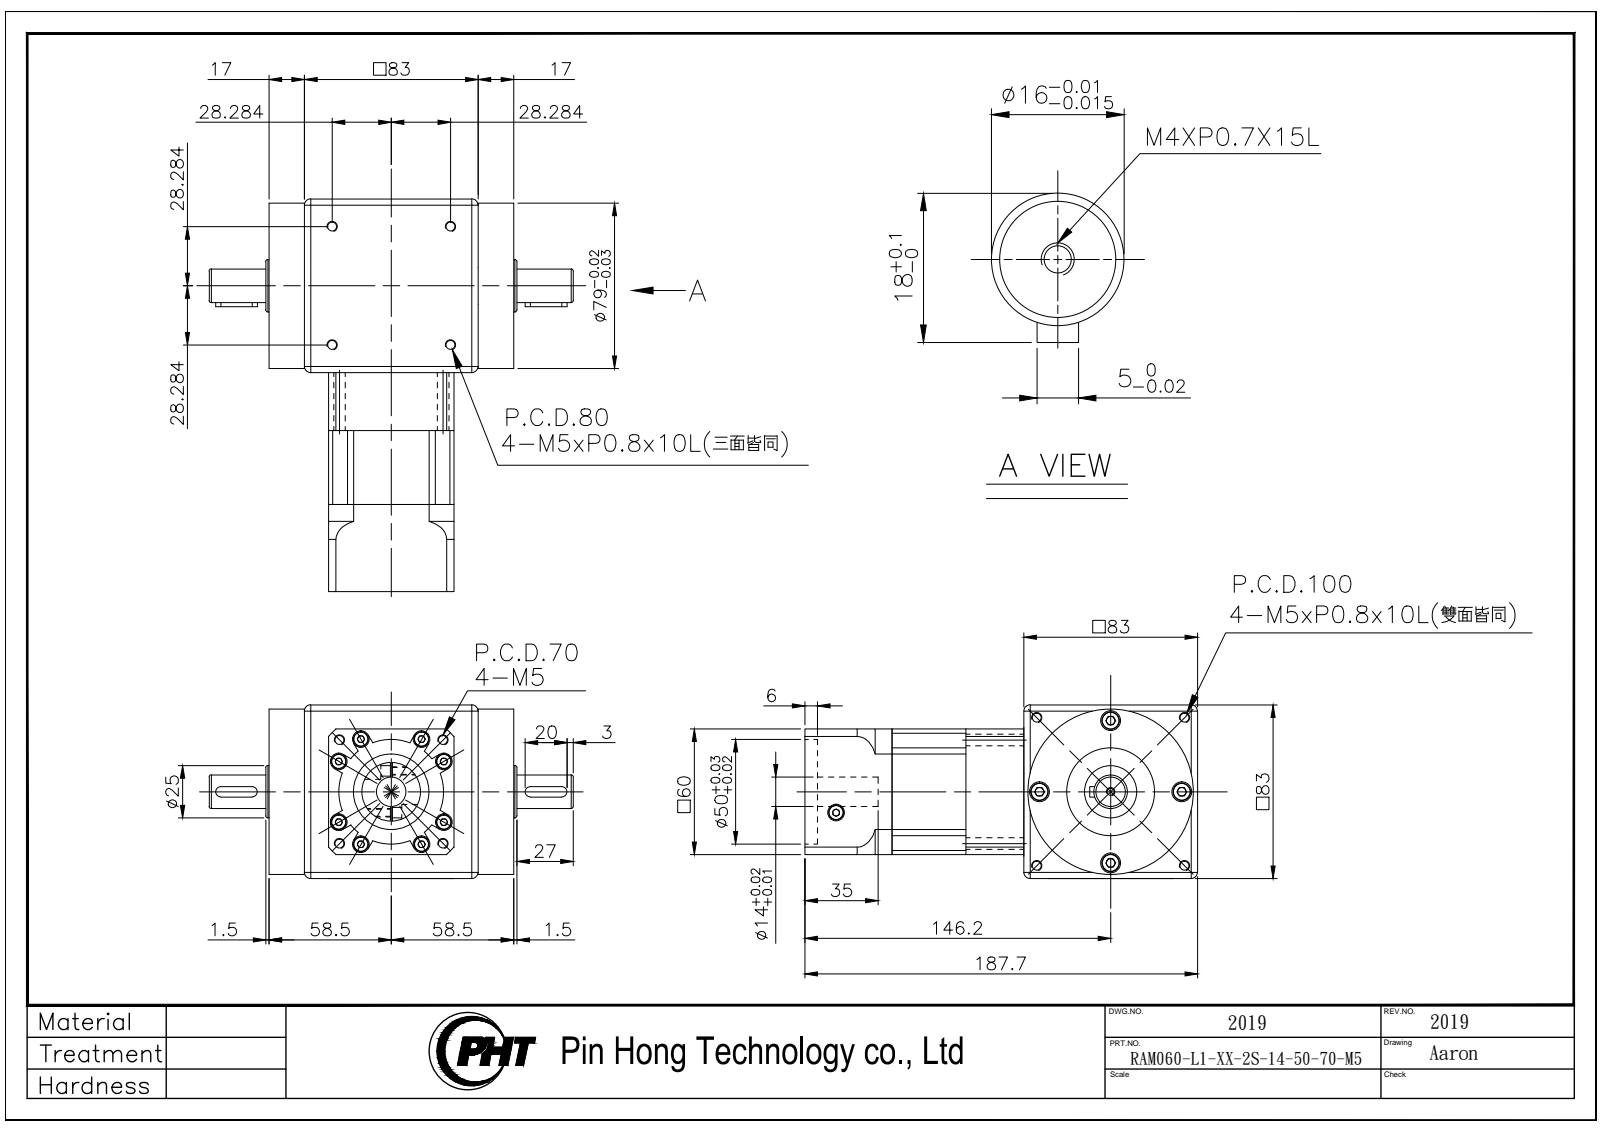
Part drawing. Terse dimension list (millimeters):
name: RAM060-L1-XX-2S-14-50-70-M5_2019
written by: SolidWorks 2016 (AUTOMOTIVE_DESIGN)
unit: mm
bodies: 5 solids, 703 faces (324 planar, 243 cylindrical, 136 other)
size: 187.7 × 174 × 83
volume: 1 060 000 mm³; area: 125 168 mm²
holes: 16× ⌀4.2, 10× ⌀8, 8× ⌀4.5, 8× ⌀5.5, 4× ⌀9.5, 1× ⌀3.3, 1× ⌀4, 1× ⌀14, 1× ⌀36
bosses: 8× ⌀8.5, 8× ⌀7, 1× ⌀79, 1× ⌀55, 1× ⌀42, 1× ⌀28, 1× ⌀25, 1× ⌀16
rounds: 4× R2.5, 4× R5, 1× R25, 1× R35, 1× R40, 1× R57.15
face distances: 83, 11.5, 71.5, 60, 27.7, 28.5, 35.35, 63.05, 88.5, 146.05
hole spacings: 29, 10.26, 14.14, 39.25, 41.01, 42.9, 50.9, 53.15
